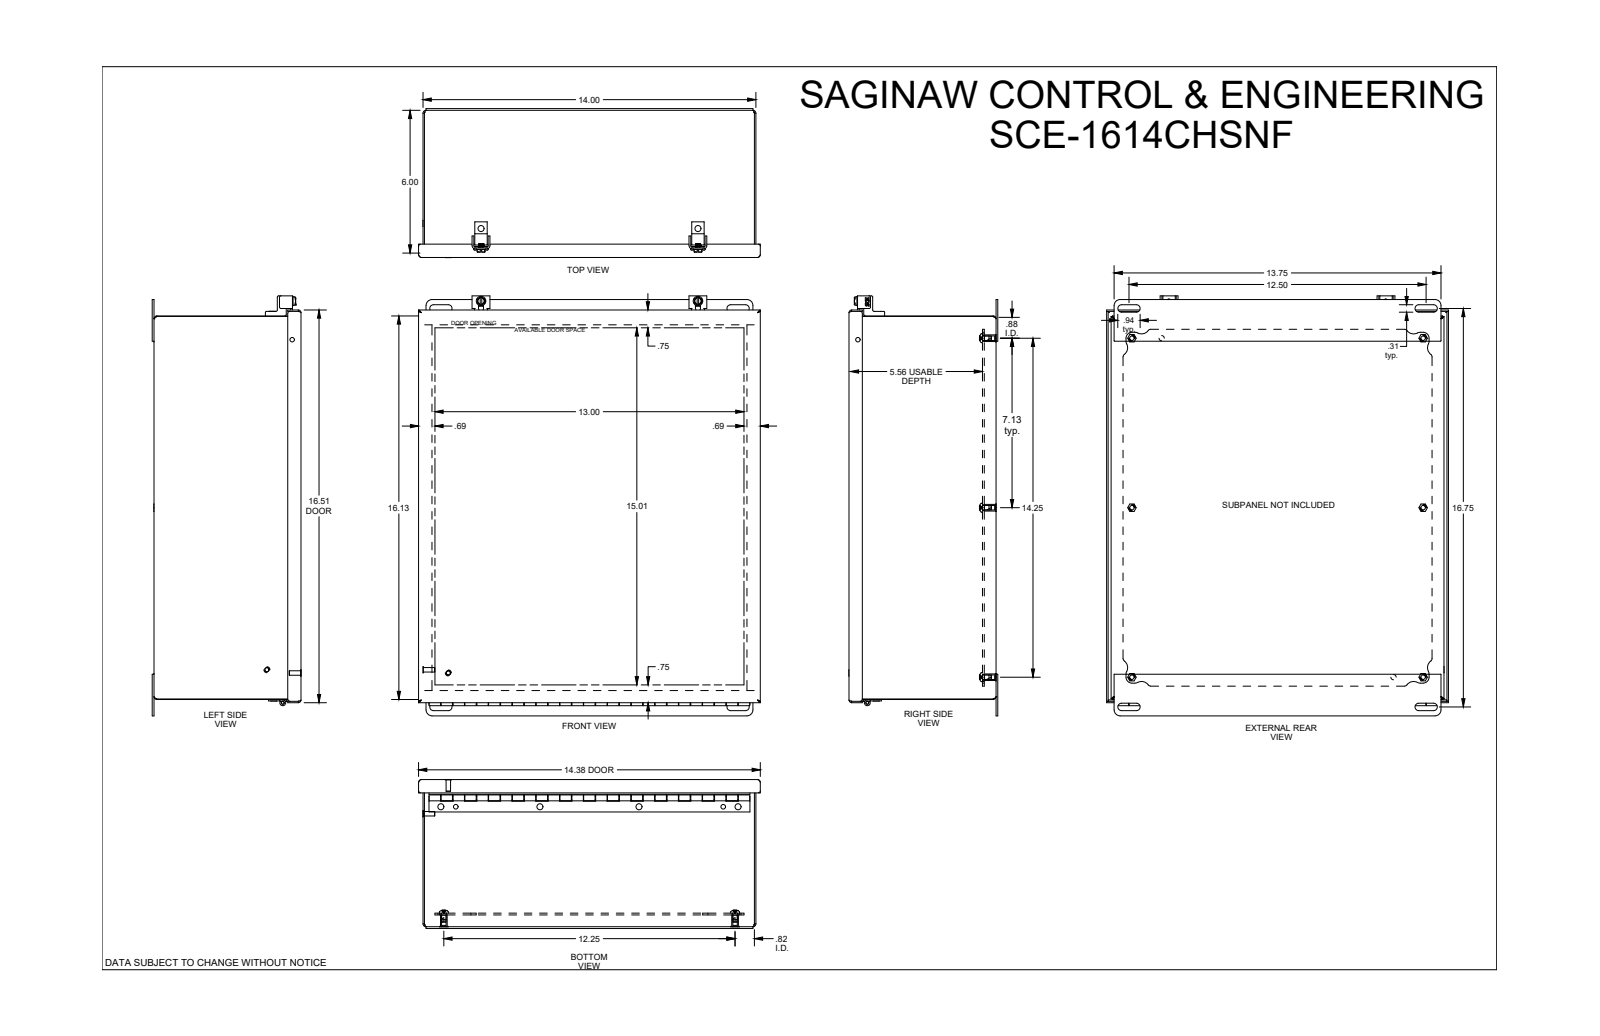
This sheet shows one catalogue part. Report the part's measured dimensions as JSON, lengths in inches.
{"part_name": "SCE-1614CHNF", "step_written_by": "SolidWorks 2019 (AUTOMOTIVE_DESIGN)", "units": "inches", "bodies": {"solids": 43, "faces": 1472, "planar": 656, "cylindrical": 387, "other": 429}, "overall_size": [17.5, 15.104, 6.265], "volume_in3": 76.15, "surface_area_in2": 2375, "round_holes": [[0.19, 12], [0.193, 8], [0.25, 6], [0.281, 4], [0.156, 2], [0.218, 2], [0.266, 2], [0.126, 1], [0.187, 1]], "round_bosses_or_shafts": [[0.188, 14], [0.256, 8], [0.373, 6], [0.28, 6], [0.396, 2], [0.188, 2], [0.246, 1], [0.123, 1]], "partial_cylinders_radius": [[0.01, 82], [0.06, 33], [0.25, 16], [0.05, 8], [0.125, 8], [0.156, 8], [0.344, 8], [0.027, 6]], "face_to_face_distances": [0.06, 6.125, 6.185, 6.065, 0.075, 0.57, 0.51, 5.555, 5.615, 0.495], "hole_center_spacings": [14.172, 14.249, 18.792, 12.25, 0.021, 1.065, 1.689, 3.146]}
